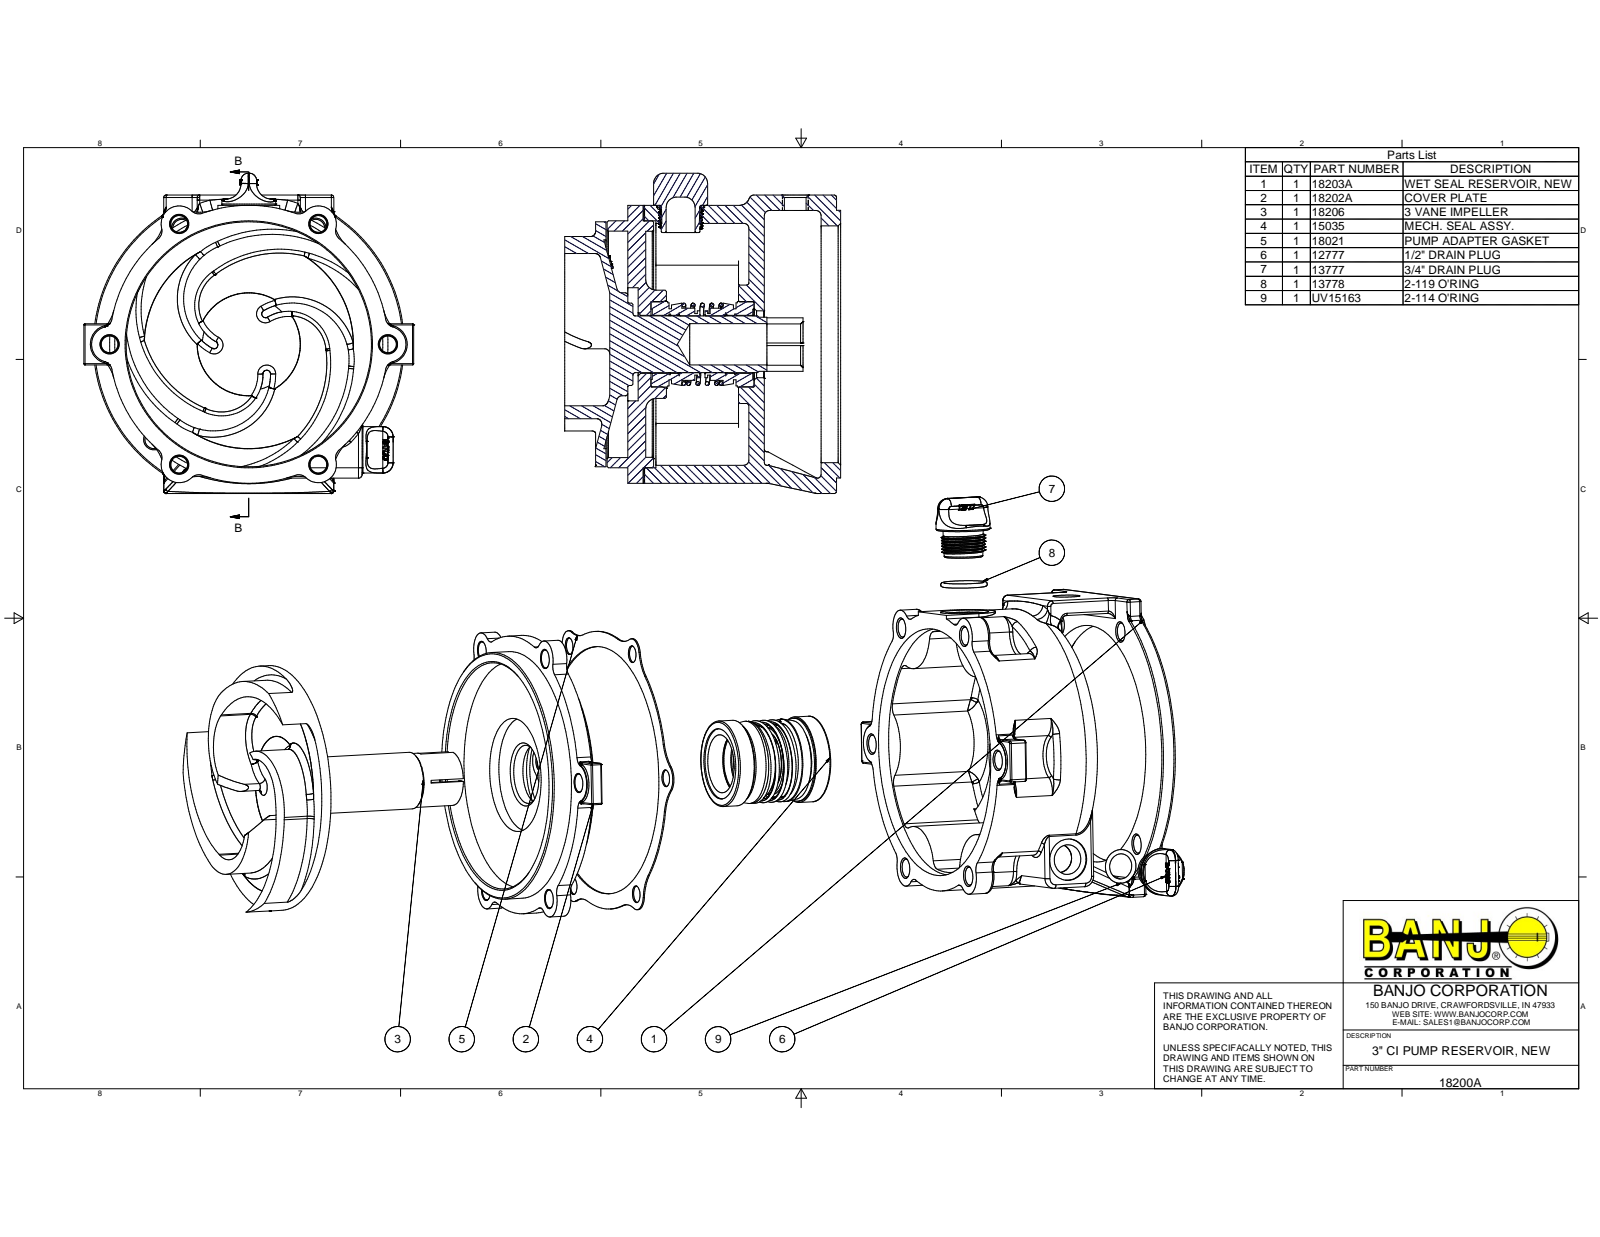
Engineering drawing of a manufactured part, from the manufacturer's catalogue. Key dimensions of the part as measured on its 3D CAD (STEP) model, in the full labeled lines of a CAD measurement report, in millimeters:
Part name (STEP PRODUCT): 18200A; 18203A; 18202A; 18206 (+6 more)
STEP written by: Autodesk Inventor 2013 (AUTOMOTIVE_DESIGN)
Units: millimetres
Bodies: 11 solids, 1460 faces (412 planar, 331 cylindrical, 717 other)
Overall size (bounding box): 203.2 × 197.6 × 170
Volume: 1 508 000 mm³ · Surface area: 383 100 mm²
Round holes (diameter × count): ⌀11.1 ×10, ⌀10.3 ×6, ⌀12.7 ×1, ⌀13.4 ×1, ⌀17.5 ×1, ⌀17.8 ×1, ⌀25.4 ×1, ⌀25.5 ×1, ⌀25.9 ×1, ⌀29.7 ×1, ⌀34.9 ×1, ⌀35.8 ×1
Round bosses / shafts (diameter × count): ⌀171.5 ×1, ⌀152.3 ×1, ⌀152.3 ×1, ⌀151.1 ×1, ⌀66.8 ×1, ⌀63.5 ×1, ⌀52.8 ×1, ⌀51.2 ×1
Partial cylindrical surfaces — rounded edges, fillets, slot ends (radius × count): R1.5 ×31, R0.8 ×28, R6.4 ×28, R25.4 ×21, R9.5 ×20, R3.2 ×16, R11.1 ×9, R15.1 ×6
Main face-to-face distances: 9.5, 84.1, 74.6, 119, 6.4, 10.3, 0.8, 73.8, 73, 68.2
Hole centre spacings: 85.7, 85.7, 148.5, 84.2, 171.5, 3.2, 21.9, 64.8
